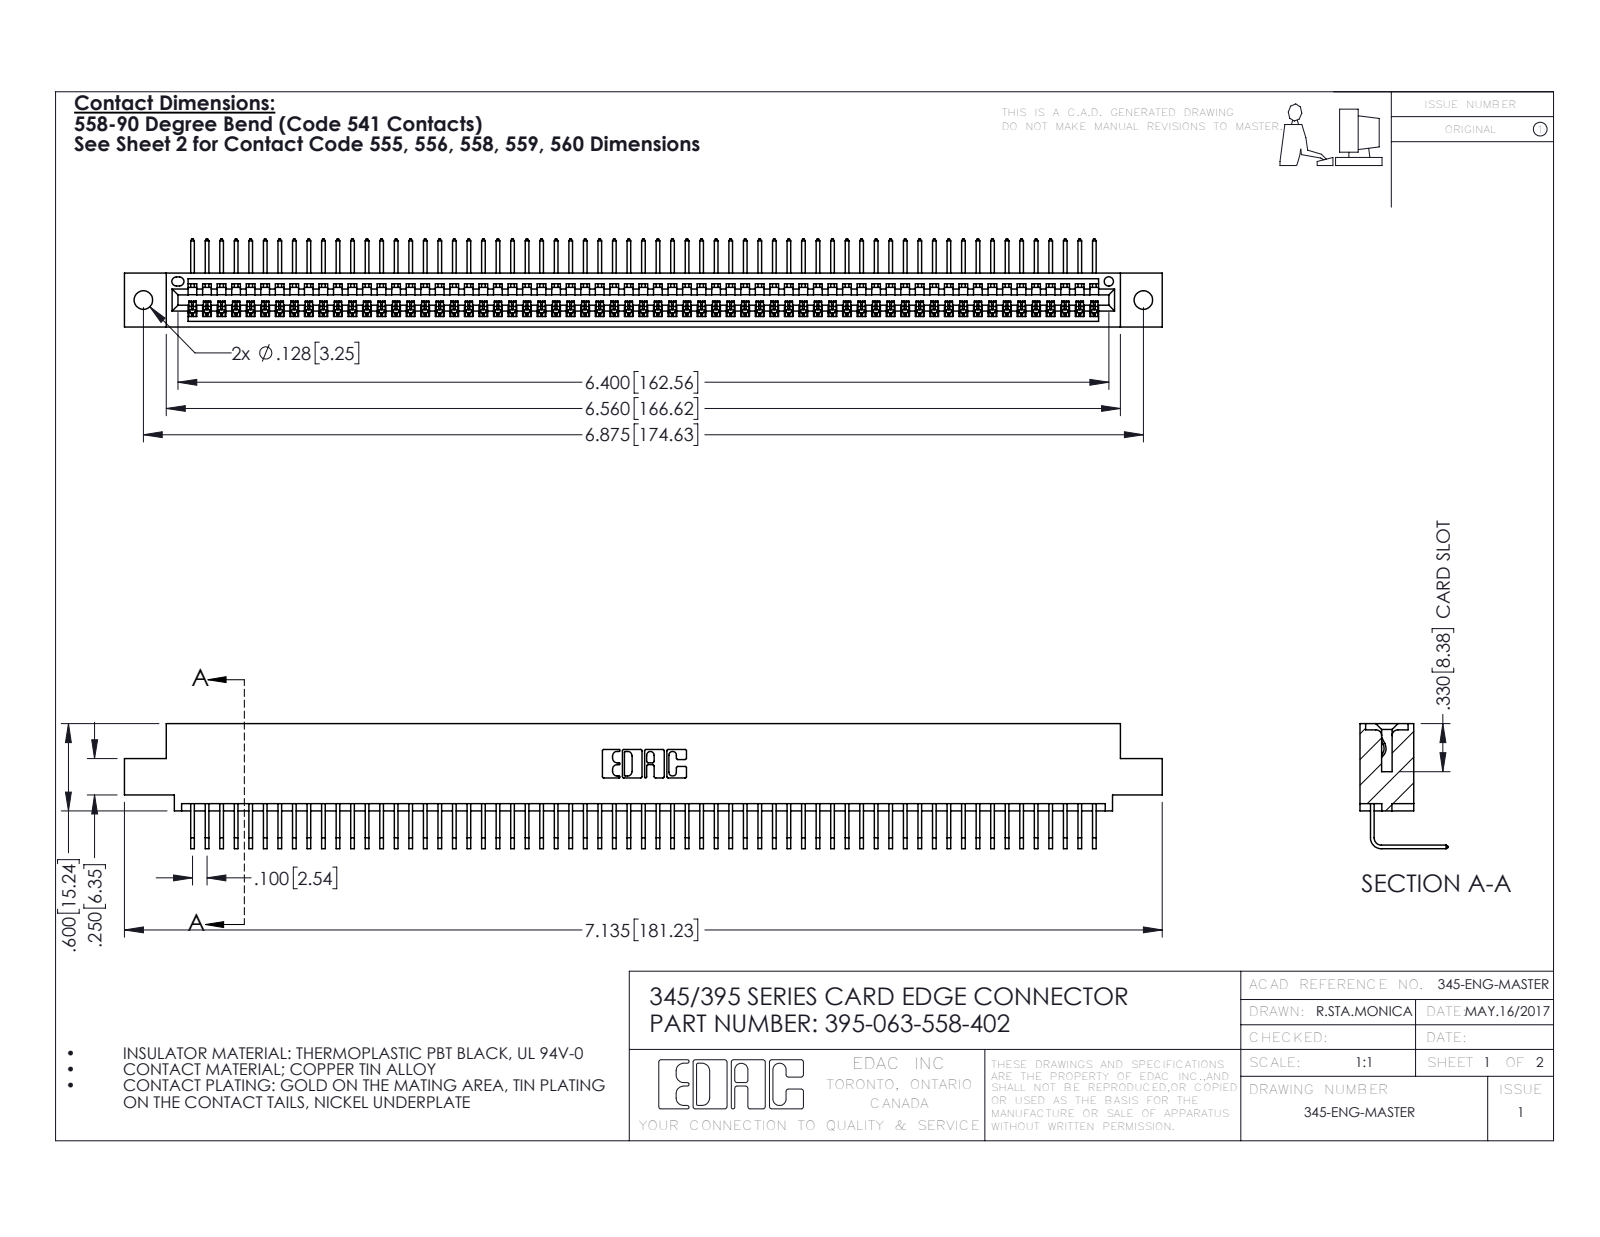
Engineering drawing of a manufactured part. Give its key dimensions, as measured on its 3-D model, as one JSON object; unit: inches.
{"part_name": "345-292-001_558 Tail - 2; 345 Part_0.110 Offset - 0.128 Dia; 395-063-558-402", "step_written_by": "SolidWorks 2016 (CONFIG_CONTROL_DESIGN)", "units": "inches", "bodies": {"solids": 64, "faces": 3910, "planar": 2730, "cylindrical": 1180, "other": 0}, "overall_size": [7.135, 0.859, 0.605], "volume_in3": 1.067, "surface_area_in2": 38.08, "round_holes": [[0.128, 2], [0.064, 1]], "partial_cylinders_radius": [[0.006, 126], [0.01, 22], [0.007, 6], [0.031, 6], [0.026, 3], [0.031, 2], [0.04, 2], [0.014, 1]], "face_to_face_distances": [0.072, 0.298, 0.37, 0.2, 0.098, 0.272, 0.025, 0.225, 0.149, 0.072], "hole_center_spacings": [0.27, 6.639, 6.875]}
